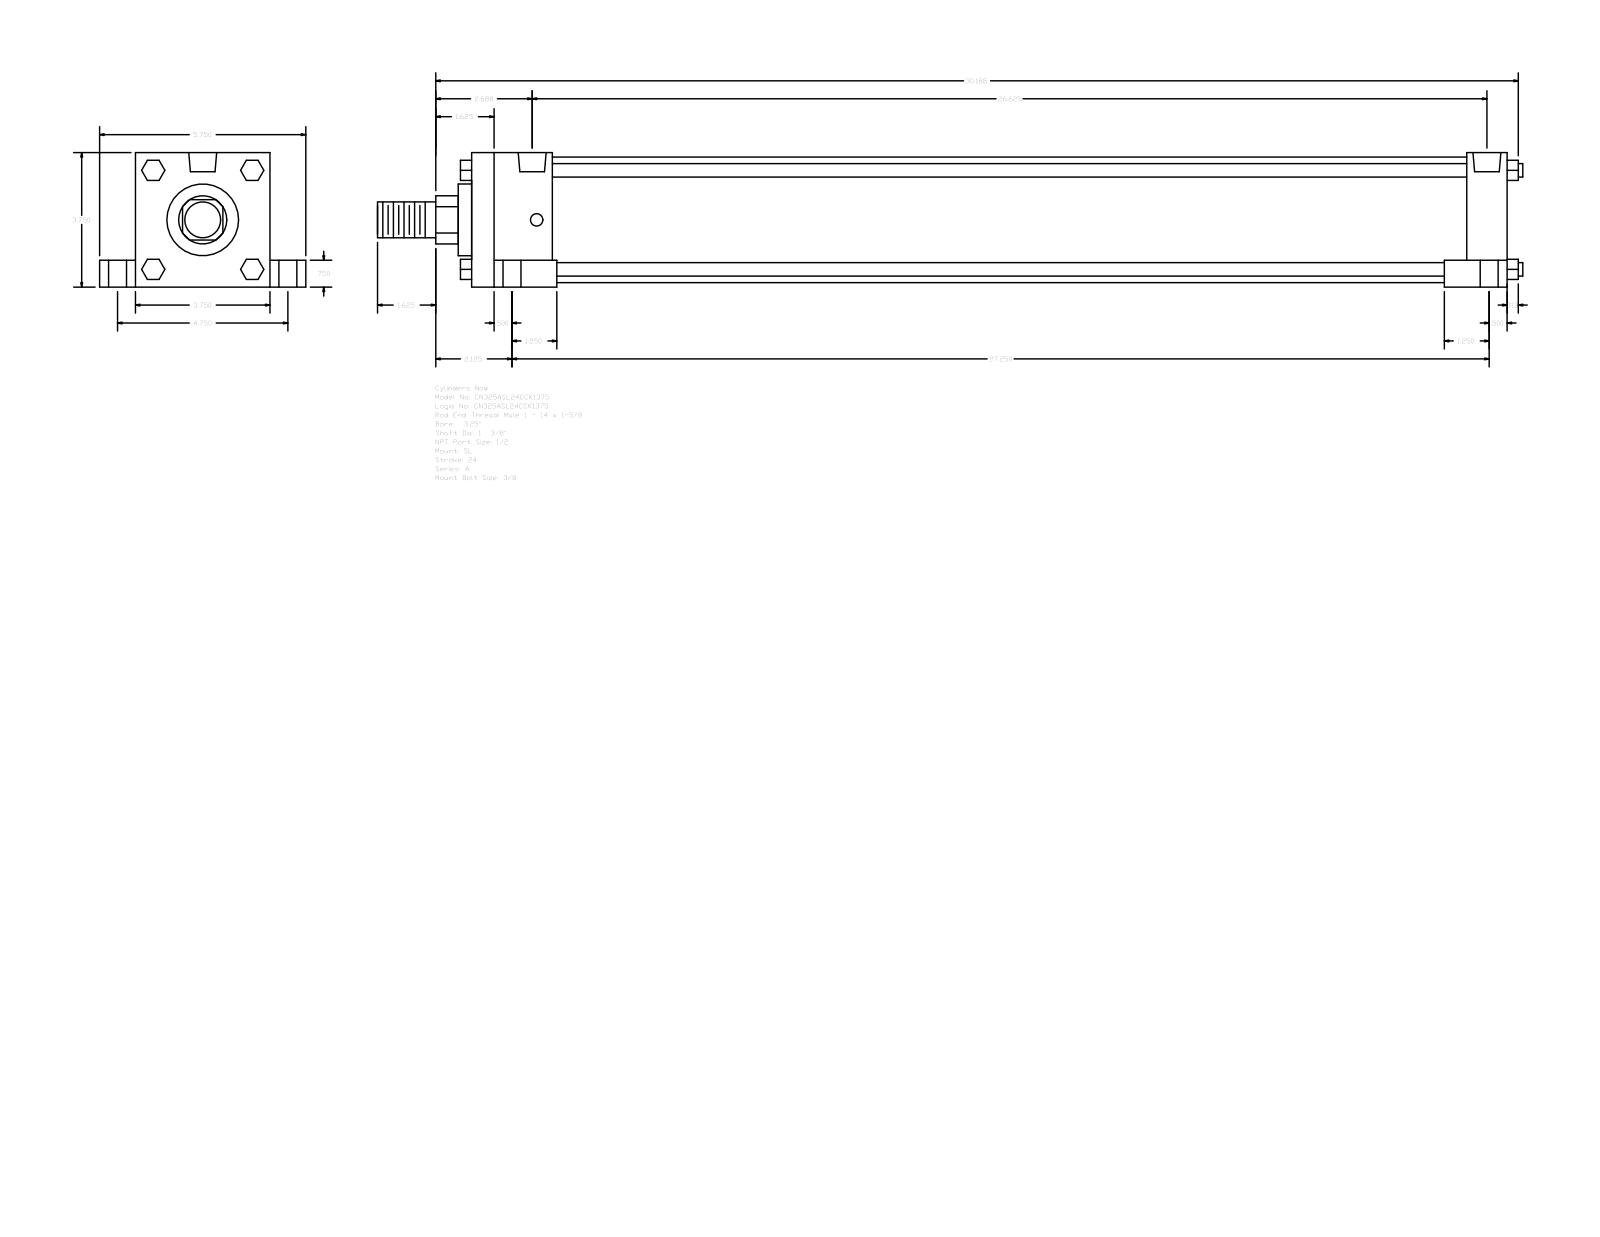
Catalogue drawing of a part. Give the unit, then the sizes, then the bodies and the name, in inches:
Units: inches
Overall size (bounding box): 31.937 × 5.75 × 3.75
Round holes (diameter × count): ⌀0.344 ×4, ⌀0.5 ×4, ⌀0.75 ×4, ⌀0.778 ×2
Round bosses / shafts (diameter × count): ⌀0.375 ×4, ⌀3.5 ×1, ⌀2 ×1, ⌀1.375 ×1, ⌀1 ×1
Partial cylindrical surfaces — rounded edges, fillets, slot ends (radius × count): R0.672 ×1
Main face-to-face distances: 3.75, 28.875, 1, 4.75, 0.75, 3, 2.25, 1.125, 27.75, 25.5
Hole centre spacings: 0.125, 2.376, 2.383, 2.441, 2.473, 4.75, 26.375, 26.5
Bodies: 0 solids, 150 faces (114 planar, 36 cylindrical, 0 other)
Part name (STEP PRODUCT): A_SL__0325_1.375
STEP written by: GSSL Pune (CONFIG_CONTROL_DESIGN)
